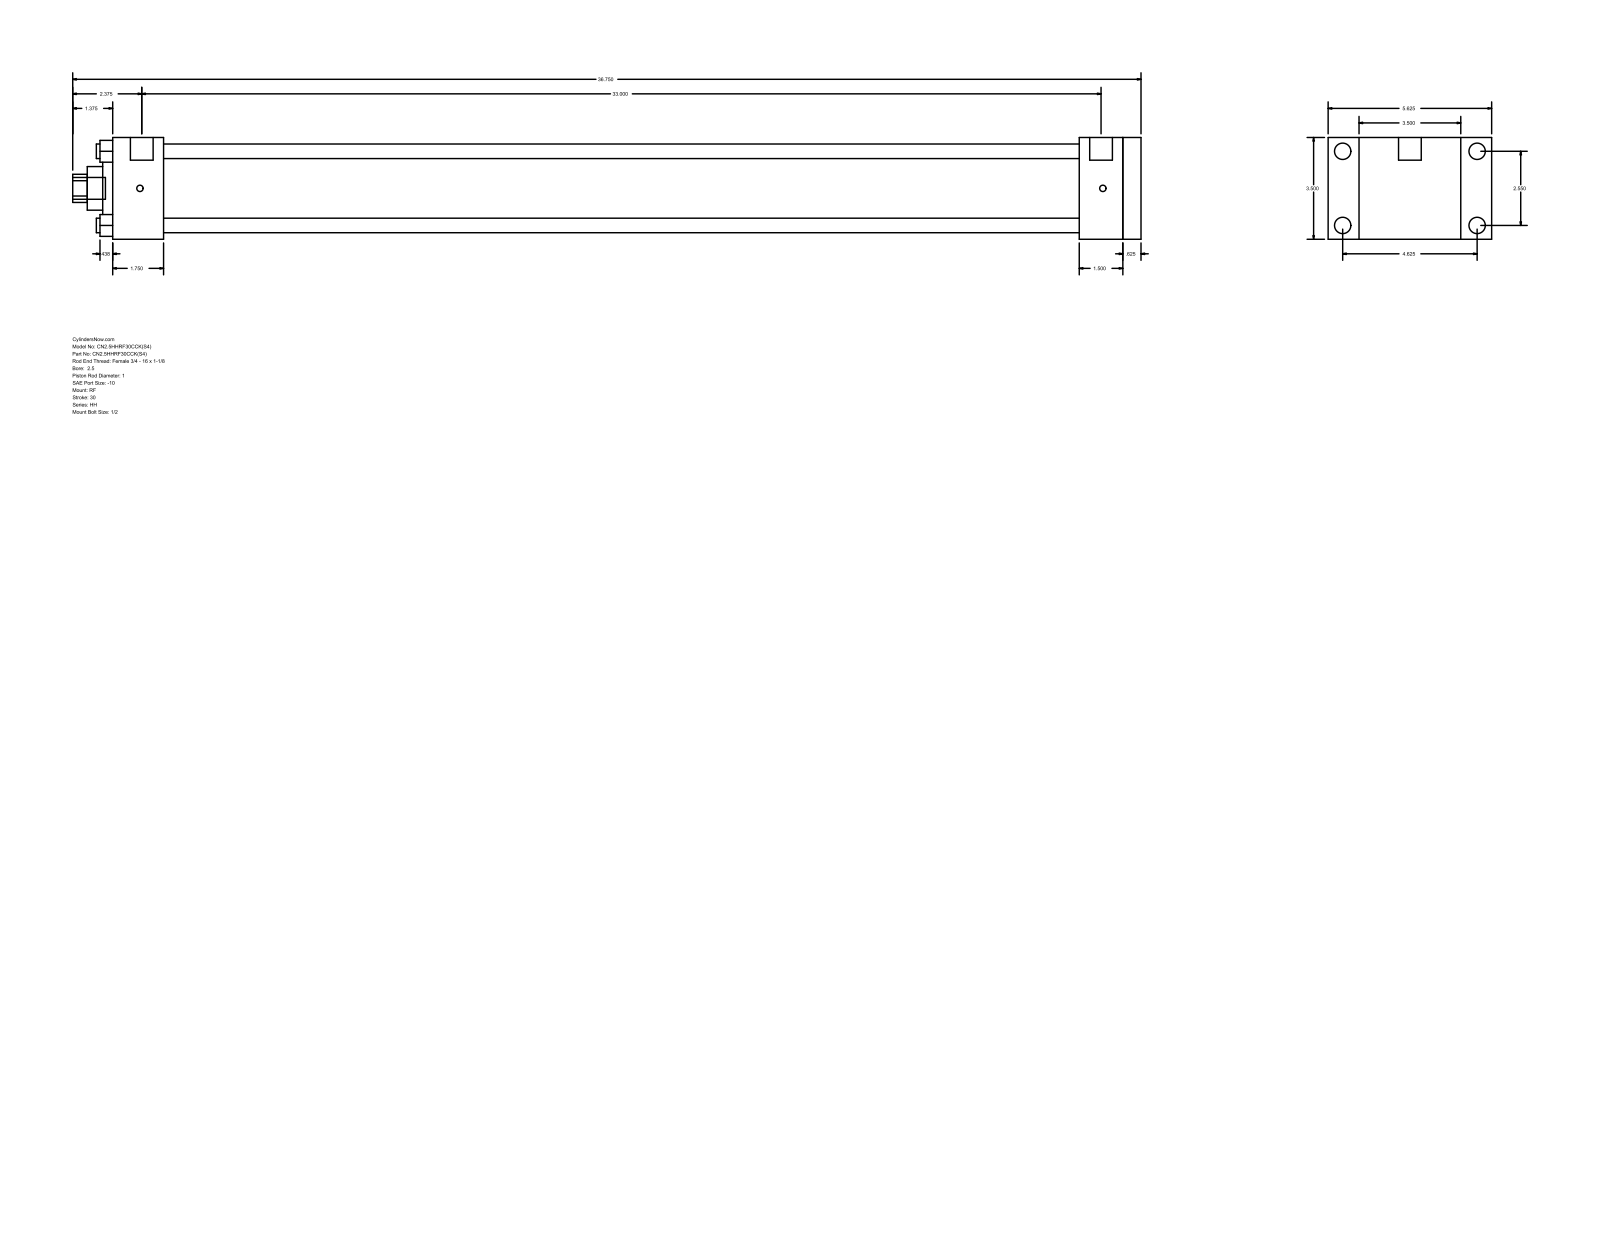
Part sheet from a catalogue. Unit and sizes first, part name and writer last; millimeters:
Units: millimetres
Overall size (bounding box): 933.45 × 142.88 × 88.9
Round holes (diameter × count): ⌀12.7 ×4, ⌀25.4 ×1, ⌀38.1 ×1, ⌀60.33 ×1, ⌀73.03 ×1
Round bosses / shafts (diameter × count): ⌀14.3 ×4, ⌀5.56 ×4, ⌀19.84 ×2, ⌀19.05 ×1
Partial cylindrical surfaces — rounded edges, fillets, slot ends (radius × count): R12.29 ×1
Main face-to-face distances: 88.9, 15.87, 882.66, 898.53, 44.46, 838.2, 854.07, 844.56, 800.1, 38.1
Hole centre spacings: 45.79, 64.76, 91.58
Bodies: 0 solids, 94 faces (65 planar, 29 cylindrical, 0 other)
Part name (STEP PRODUCT): HH_RF__0250_1
STEP written by: GSSL Pune (CONFIG_CONTROL_DESIGN)
